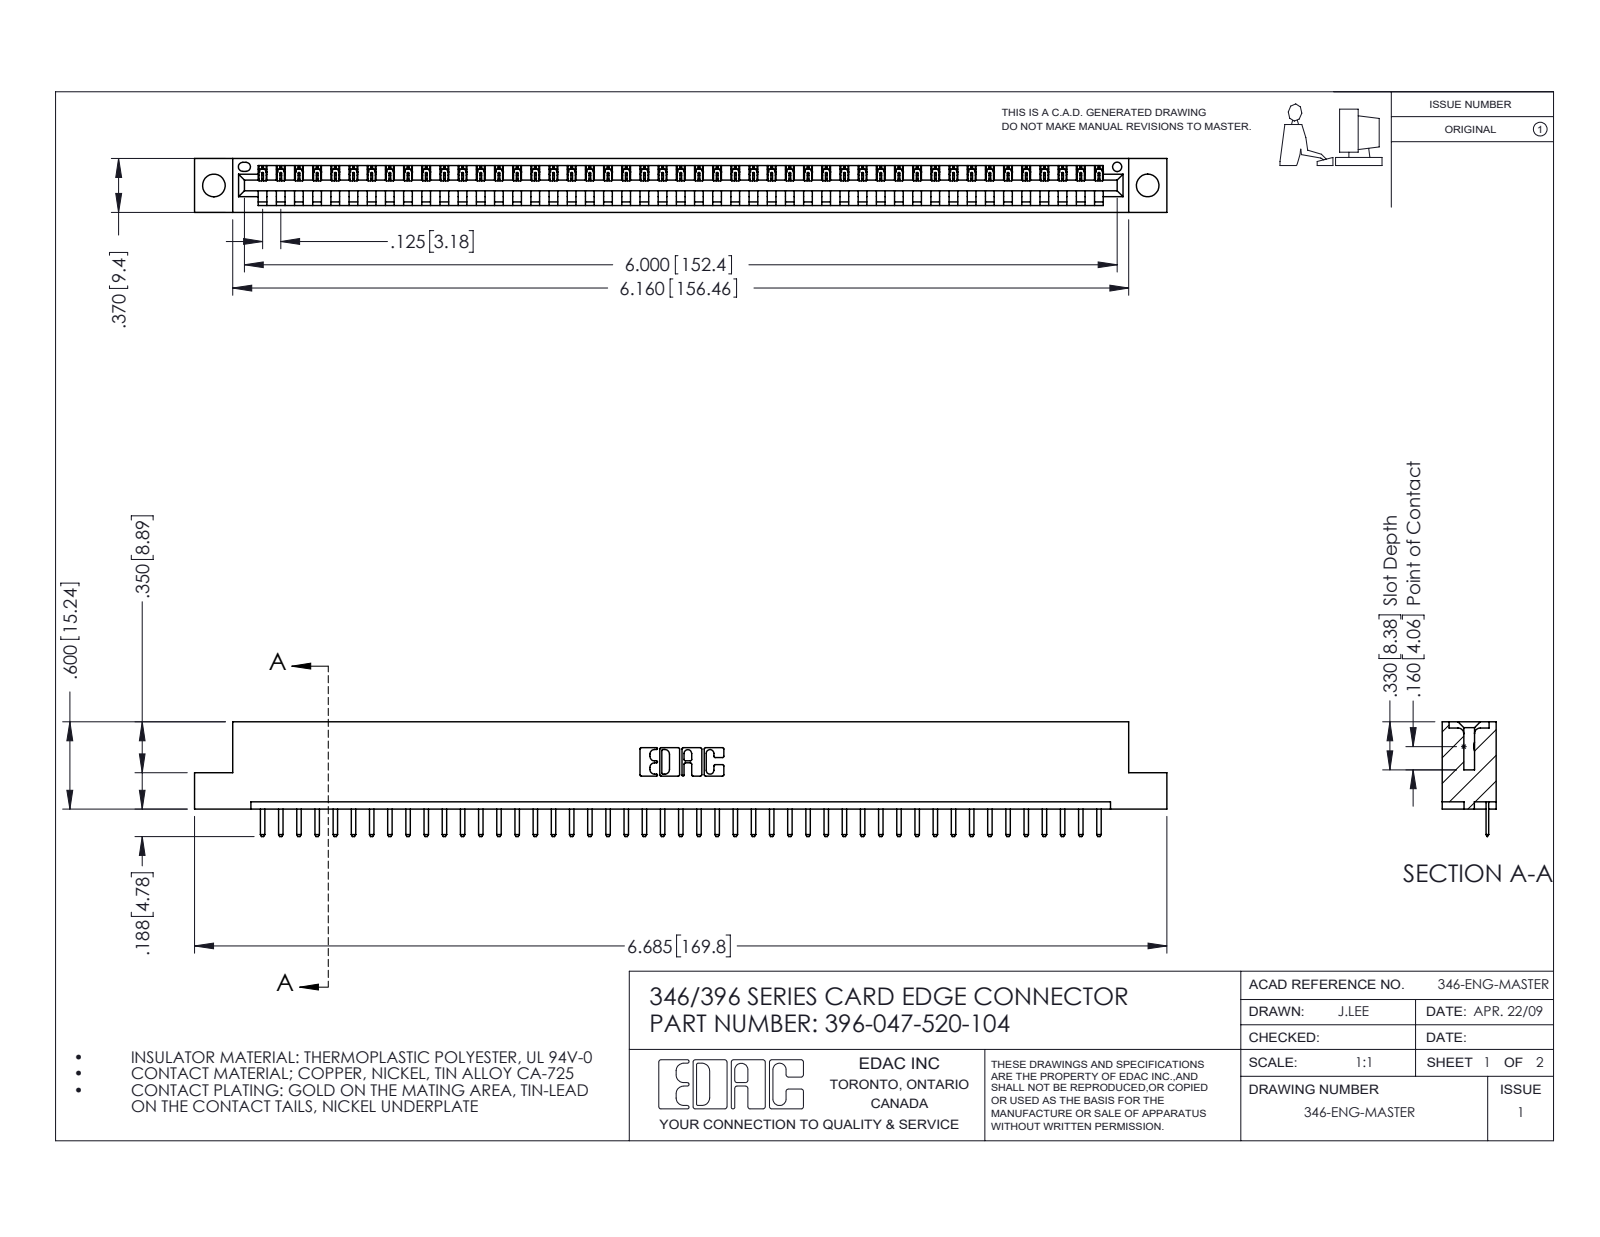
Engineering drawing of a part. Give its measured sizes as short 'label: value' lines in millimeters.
name: 396-047-520-104; 346 Part_Flush Mounting Lugs - 0.156 Dia-TH; 345-292-001_345-293-120
written by: SolidWorks 2016 (CONFIG_CONTROL_DESIGN)
unit: mm
bodies: 48 solids, 3036 faces (2050 planar, 986 cylindrical, 0 other)
size: 169.8 × 20 × 9.4
volume: 16 100 mm³; area: 19 480 mm²
holes: 2× ⌀4, 1× ⌀1.6
rounds: 96× R0.3, 94× R0.2, 22× R0.3, 6× R0.2, 6× R0.8, 3× R0.7, 2× R0.8, 2× R1
face distances: 1.2, 8.2, 9.4, 6.4, 3.8, 5.6, 2.5, 4.4, 1.8, 7.6
hole spacings: 6.2, 157.8, 163.1
